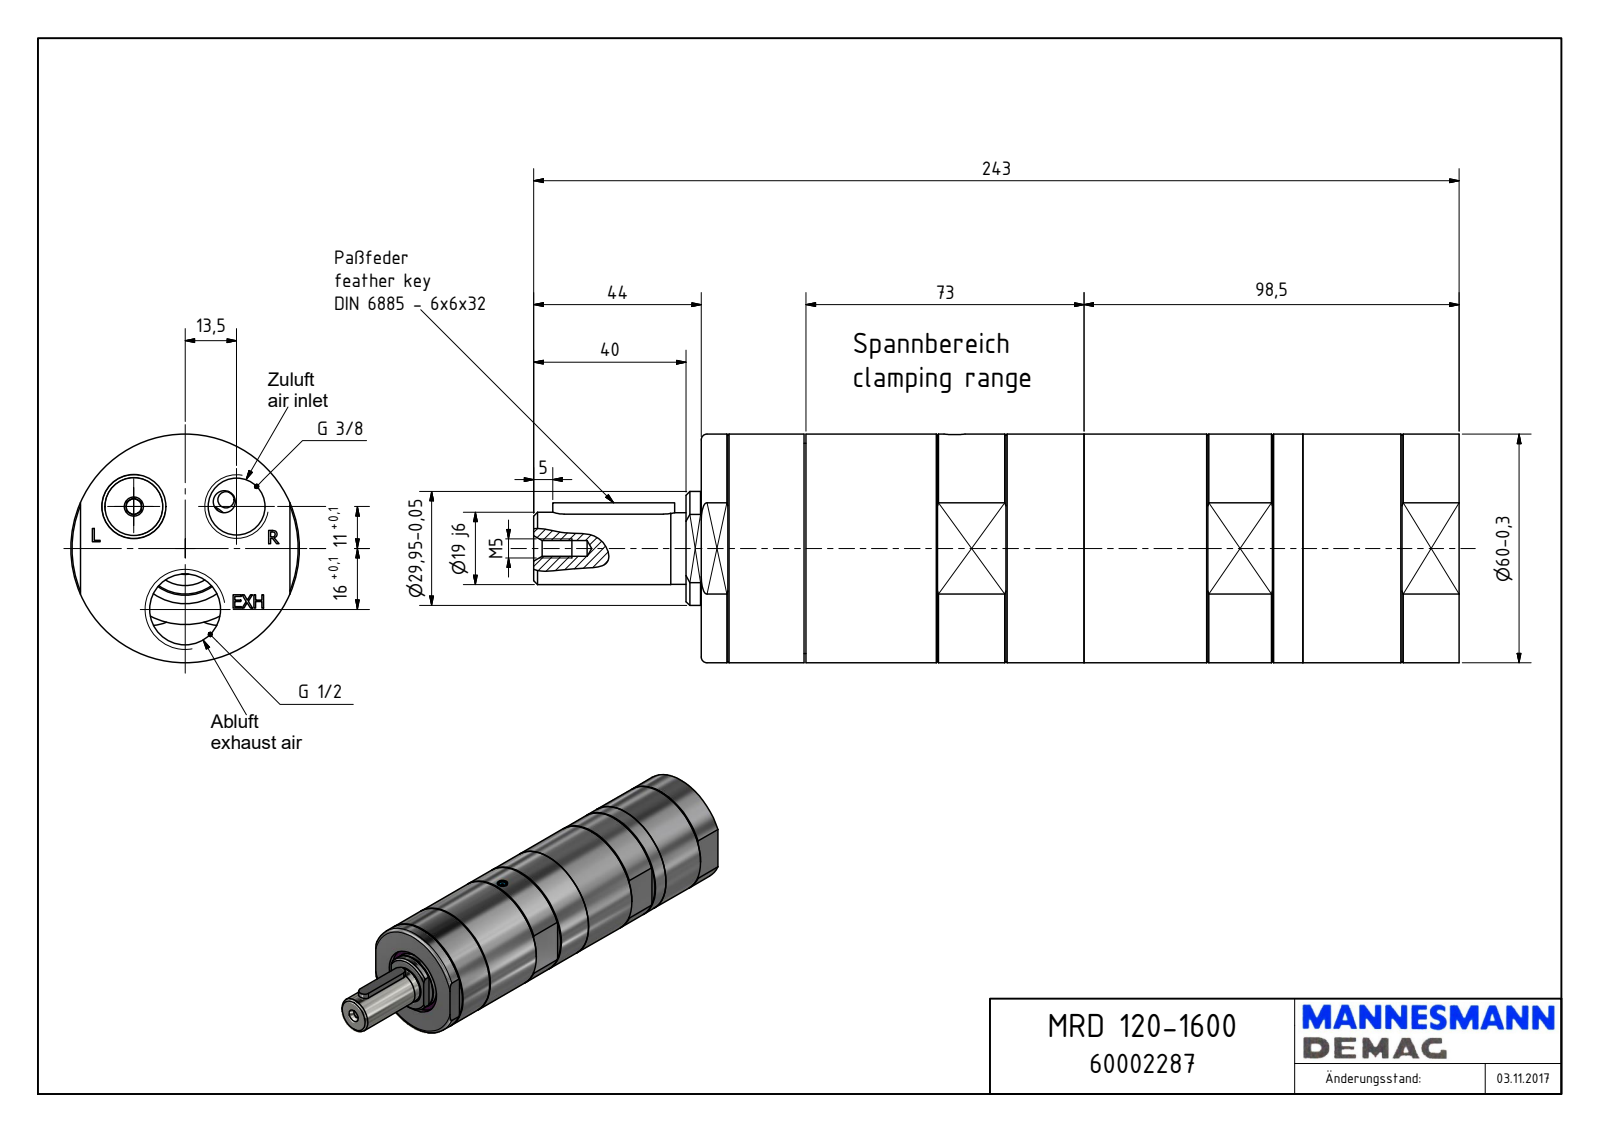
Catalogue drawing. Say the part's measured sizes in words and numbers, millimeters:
The part is named "MRD 120-1600_60002287". Its 3-D file was written by "Autodesk Inventor 2018 (AUTOMOTIVE_DESIGN)". It is 1 solid with 220 faces: 124 planar, 47 cylindrical and 49 other. Overall it measures 243 by 60 by 60 millimeters. Its volume is 559 157 cubic millimeters and its surface area 54 149 square millimeters. Round holes: 2 of diameter 4, 2 of diameter 14.95, 1 of diameter 1.55, 1 of diameter 4.13, 1 of diameter 5.5, 1 of diameter 18.63, 1 of diameter 35, 1 of diameter 55.38, 1 of diameter 57. Round bosses or shafts: 1 of diameter 60, 1 of diameter 55.18, 1 of diameter 52.91, 1 of diameter 29.95, 1 of diameter 19, 1 of diameter 18.8, 1 of diameter 5, 1 of diameter 3.6. Partial cylindrical surfaces (rounded edges, fillets, slot ends): 2 of radius 3, 2 of radius 7.5, 1 of radius 8.5, 1 of radius 19.14, 1 of radius 23.5. The main face-to-face distances are 199, 55, 183.06, 15.94, 15, 16.5, 171.5, 186, 2.94, 13. The hole center spacings are 17.41, 30.19, 16, 27.
